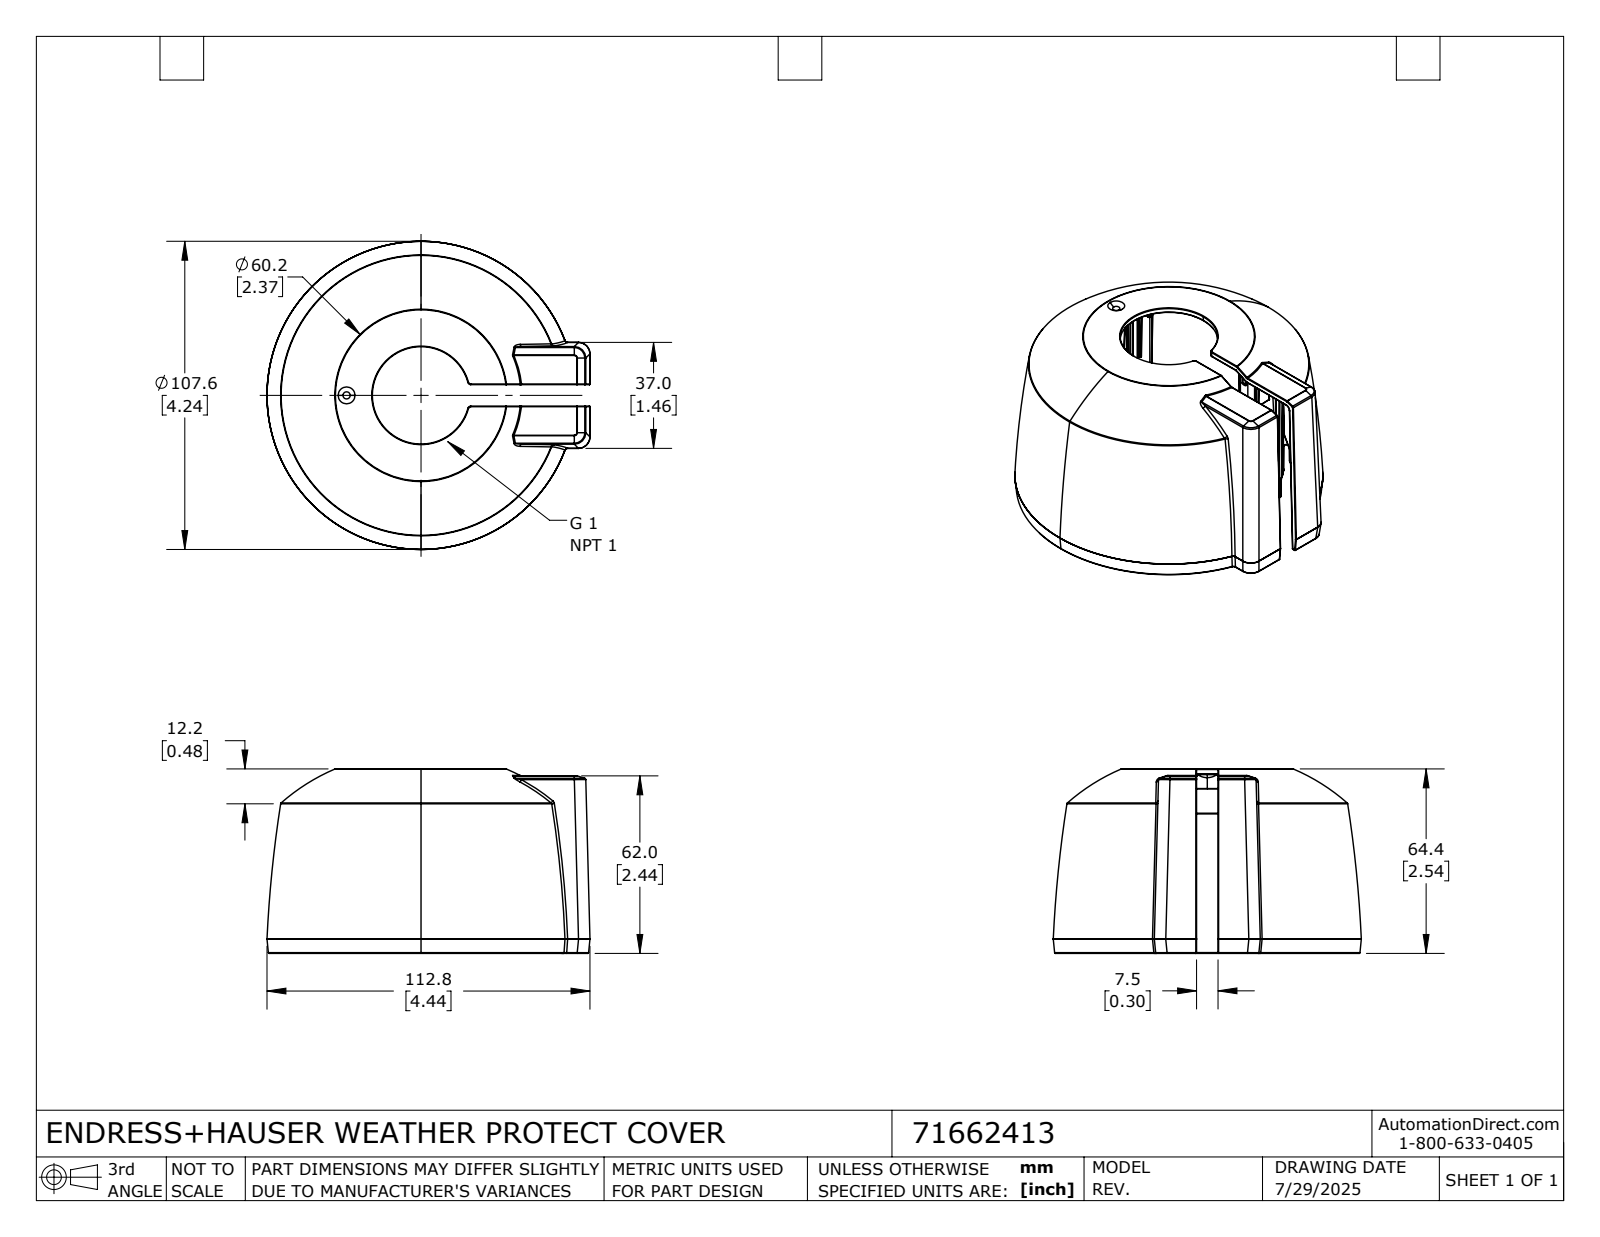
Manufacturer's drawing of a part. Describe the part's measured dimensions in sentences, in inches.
The part is named "71662413". Its 3-D file was written by "SolidWorks 2024 (AUTOMOTIVE_DESIGN)". It is 1 solid with 1604 faces: 235 planar, 201 cylindrical and 1168 other. Overall it measures 4.441 by 4.236 by 2.535 inches. Its volume is 3.583 cubic inches and its surface area 101.1 square inches. Round holes: 1 of diameter 1.339. Round bosses or shafts: 1 of diameter 0.236. Partial cylindrical surfaces (rounded edges, fillets, slot ends): 63 of radius 0.01, 22 of radius 0.016, 20 of radius 0.039, 14 of radius 0.012, 10 of radius 0.004, 10 of radius 0.008, 9 of radius 0.02, 4 of radius 0.157. The main face-to-face distances are 0.079, 0.094, 0.016, 0.173, 0.022, 2.535, 2.457, 2.441, 2.362, 0.619.
